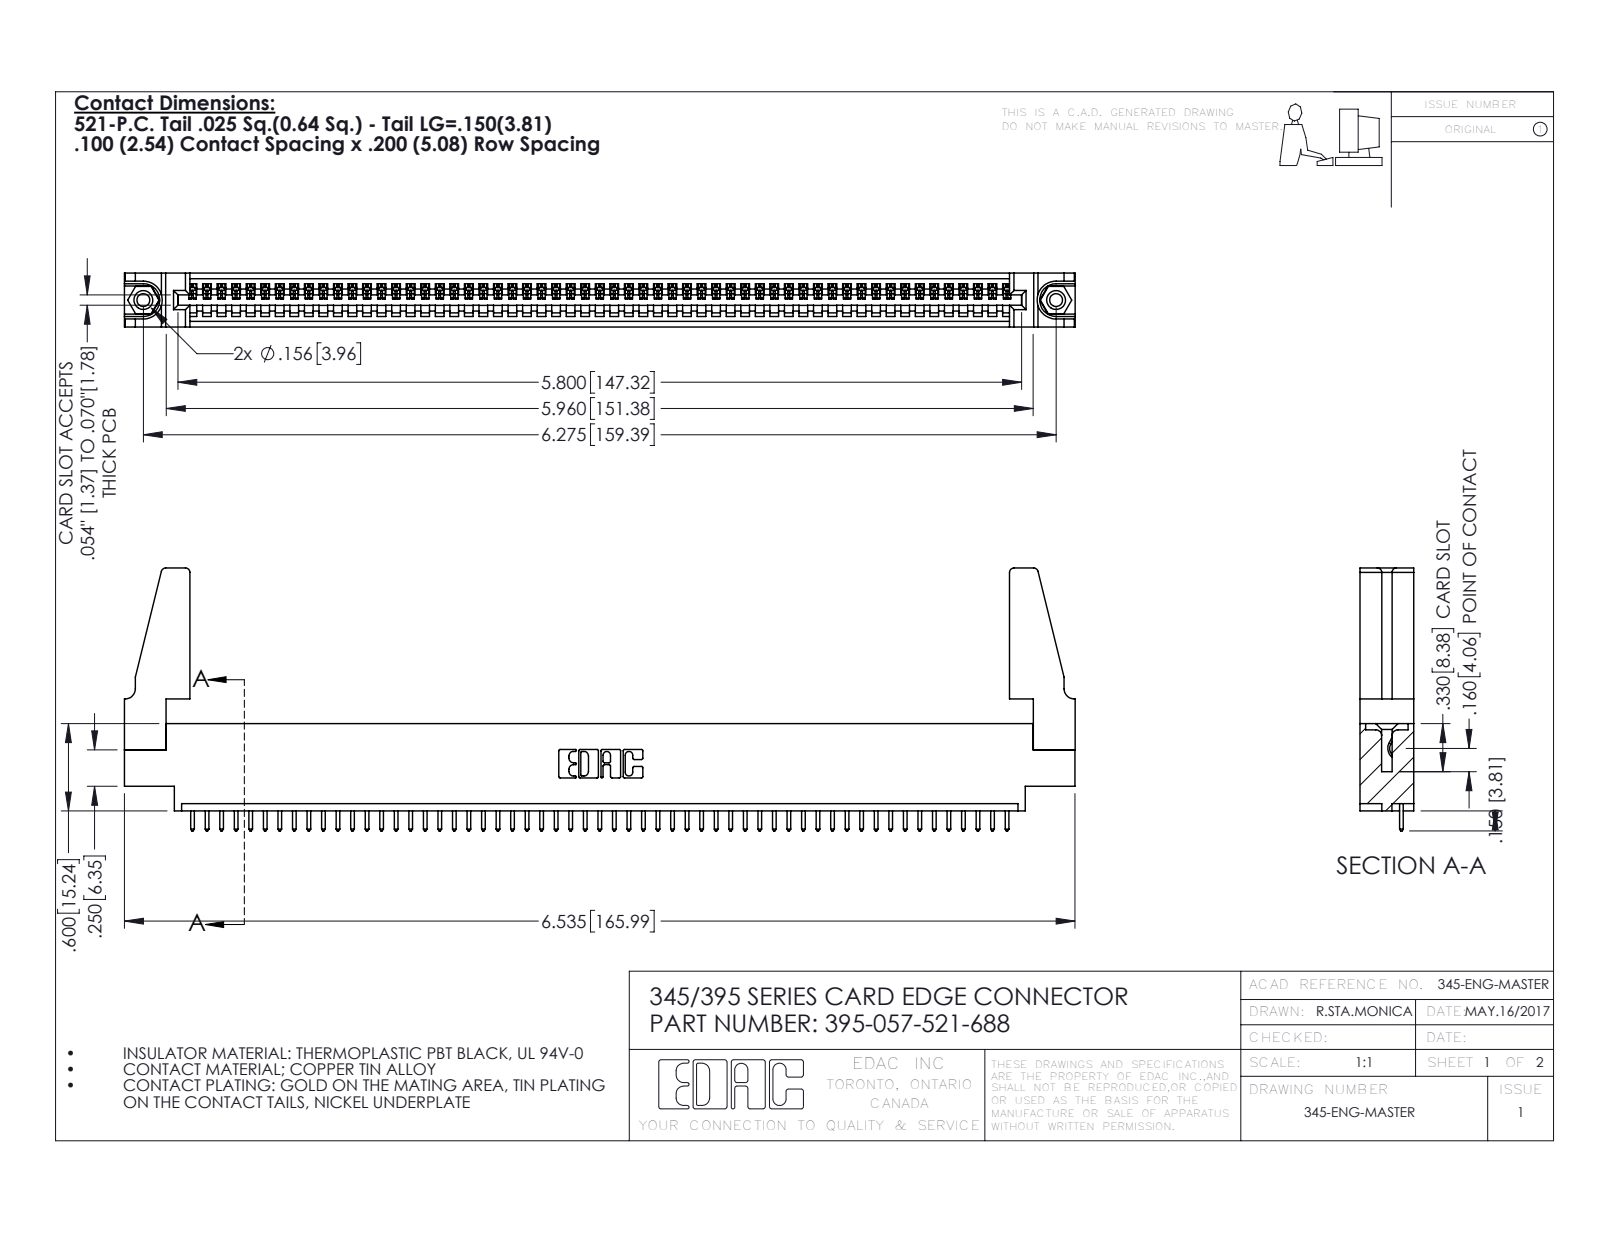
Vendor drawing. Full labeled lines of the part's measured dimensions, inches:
Part name (STEP PRODUCT): 345-220-078_345-220-088; 345-250-001_345-250-001-102; 345 Part_0.170 Offset - 0.156 Dia-TH; 395-057-521-688 (+1 more)
STEP written by: SolidWorks 2016 (CONFIG_CONTROL_DESIGN)
Units: inches
Bodies: 62 solids, 3560 faces (2436 planar, 1108 cylindrical, 16 other)
Overall size (bounding box): 6.536 × 1.807 × 0.37
Volume: 1.151 in³ · Surface area: 36.54 in²
Round holes (diameter × count): ⌀0.089 ×2, ⌀0.125 ×2, ⌀0.156 ×2, ⌀0.064 ×1
Round bosses / shafts (diameter × count): ⌀0.155 ×2
Partial cylindrical surfaces — rounded edges, fillets, slot ends (radius × count): R0.006 ×114, R0.01 ×114, R0.01 ×22, R0.03 ×8, R0.007 ×6, R0.031 ×6, R0.026 ×3, R0.031 ×2
Main face-to-face distances: 0.072, 0.298, 0.37, 0.2, 0.098, 0.272, 0.025, 0.225, 0.175, 0.149
Hole centre spacings: 0.27, 6.039, 6.275
